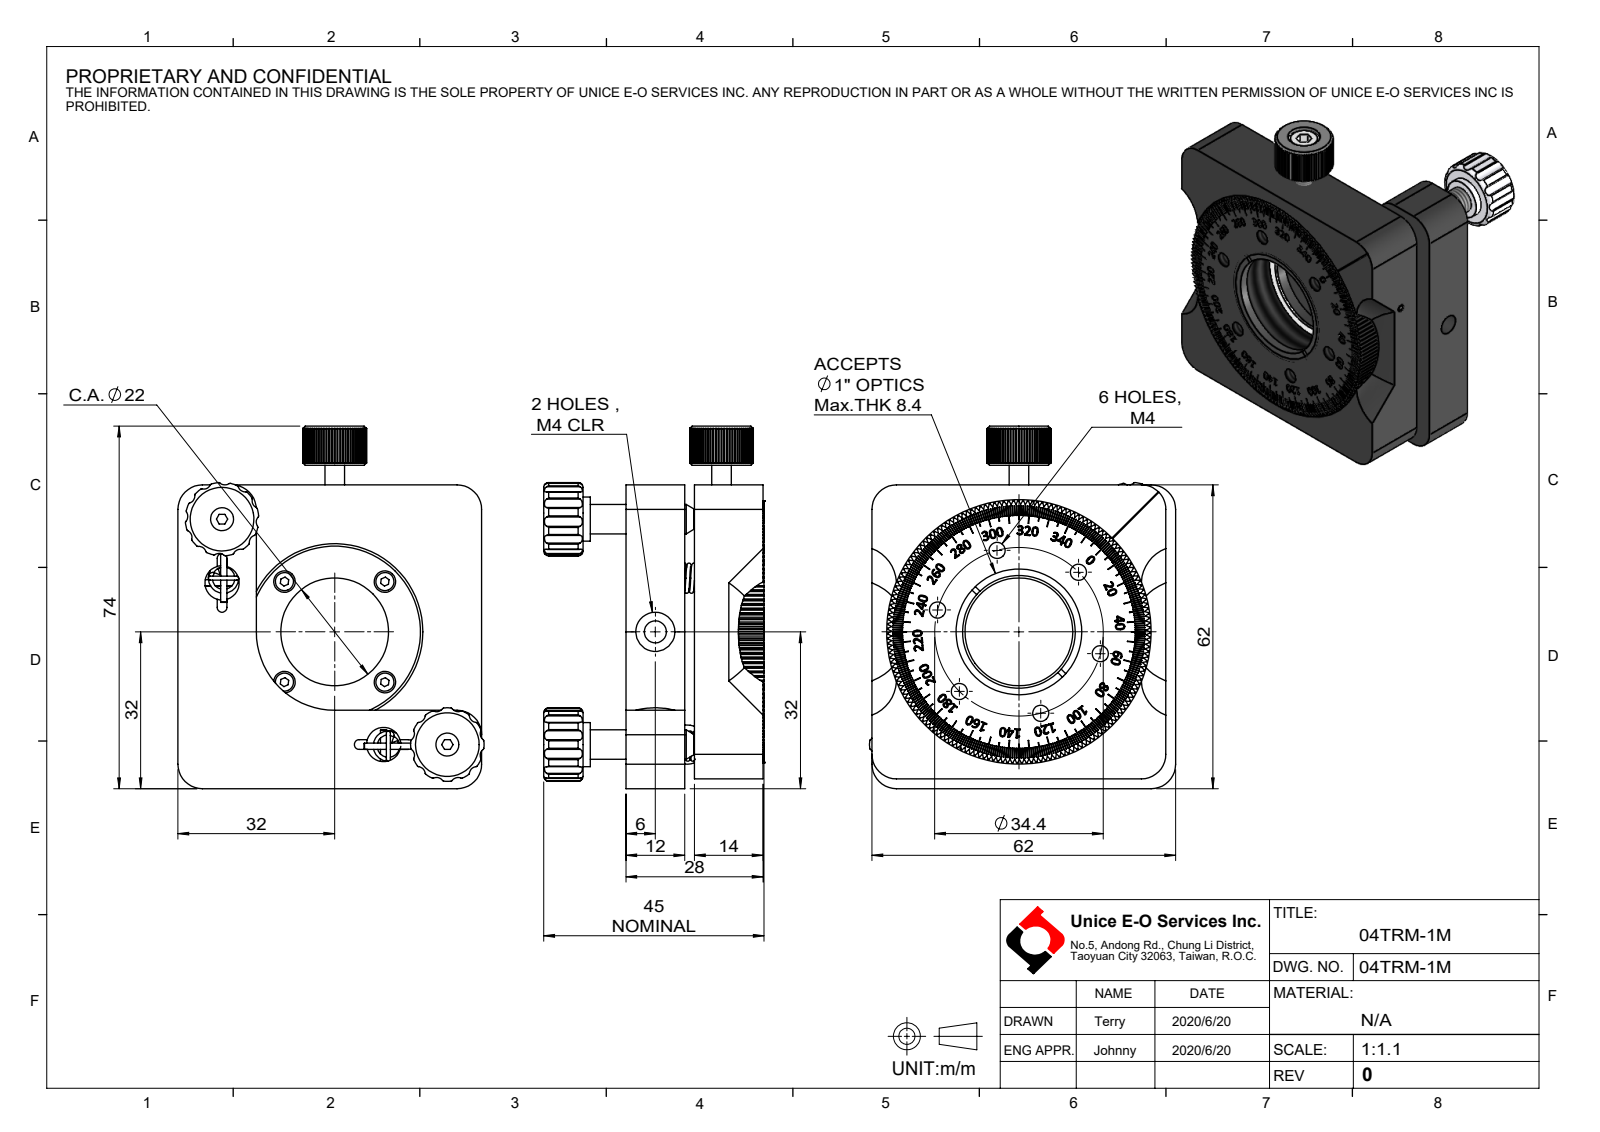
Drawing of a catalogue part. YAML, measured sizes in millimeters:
part_name: "04TRM-1M"
step_written_by: "SolidWorks 2016 (CONFIG_CONTROL_DESIGN)"
units: millimeters
bodies: {solids: 0, faces: 2210, planar: 1435, cylindrical: 516, other: 259}
overall_size: [73.98, 62.5, 44.97]
round_holes:
  - {diameter: 3.3, count: 6}
  - {diameter: 4.4, count: 4}
  - {diameter: 1, count: 2}
  - {diameter: 1.7, count: 2}
  - {diameter: 4.5, count: 2}
  - {diameter: 4.7, count: 2}
  - {diameter: 7, count: 2}
  - {diameter: 8, count: 2}
  - {diameter: 9.5, count: 2}
  - {diameter: 7.2, count: 1}
  - {diameter: 22, count: 1}
  - {diameter: 23, count: 1}
round_bosses_or_shafts:
  - {diameter: 3.7, count: 4}
  - {diameter: 1.3, count: 4}
  - {diameter: 9, count: 2}
  - {diameter: 6, count: 2}
  - {diameter: 35, count: 1}
  - {diameter: 4, count: 1}
partial_cylinders:
  - {radius: 0.1, count: 51}
  - {radius: 0.3, count: 48}
  - {radius: 1.5, count: 24}
  - {radius: 5, count: 9}
  - {radius: 1, count: 4}
  - {radius: 7.5, count: 2}
  - {radius: 6.5, count: 1}
  - {radius: 16, count: 1}
face_to_face_distances: [14, 2, 16, 12, 14.2, 28.2, 16.2, 60, 62, 28]
hole_center_spacings: [17.2, 17.21, 8.61, 14.5, 16.02, 20.5, 22.49, 27.49]
